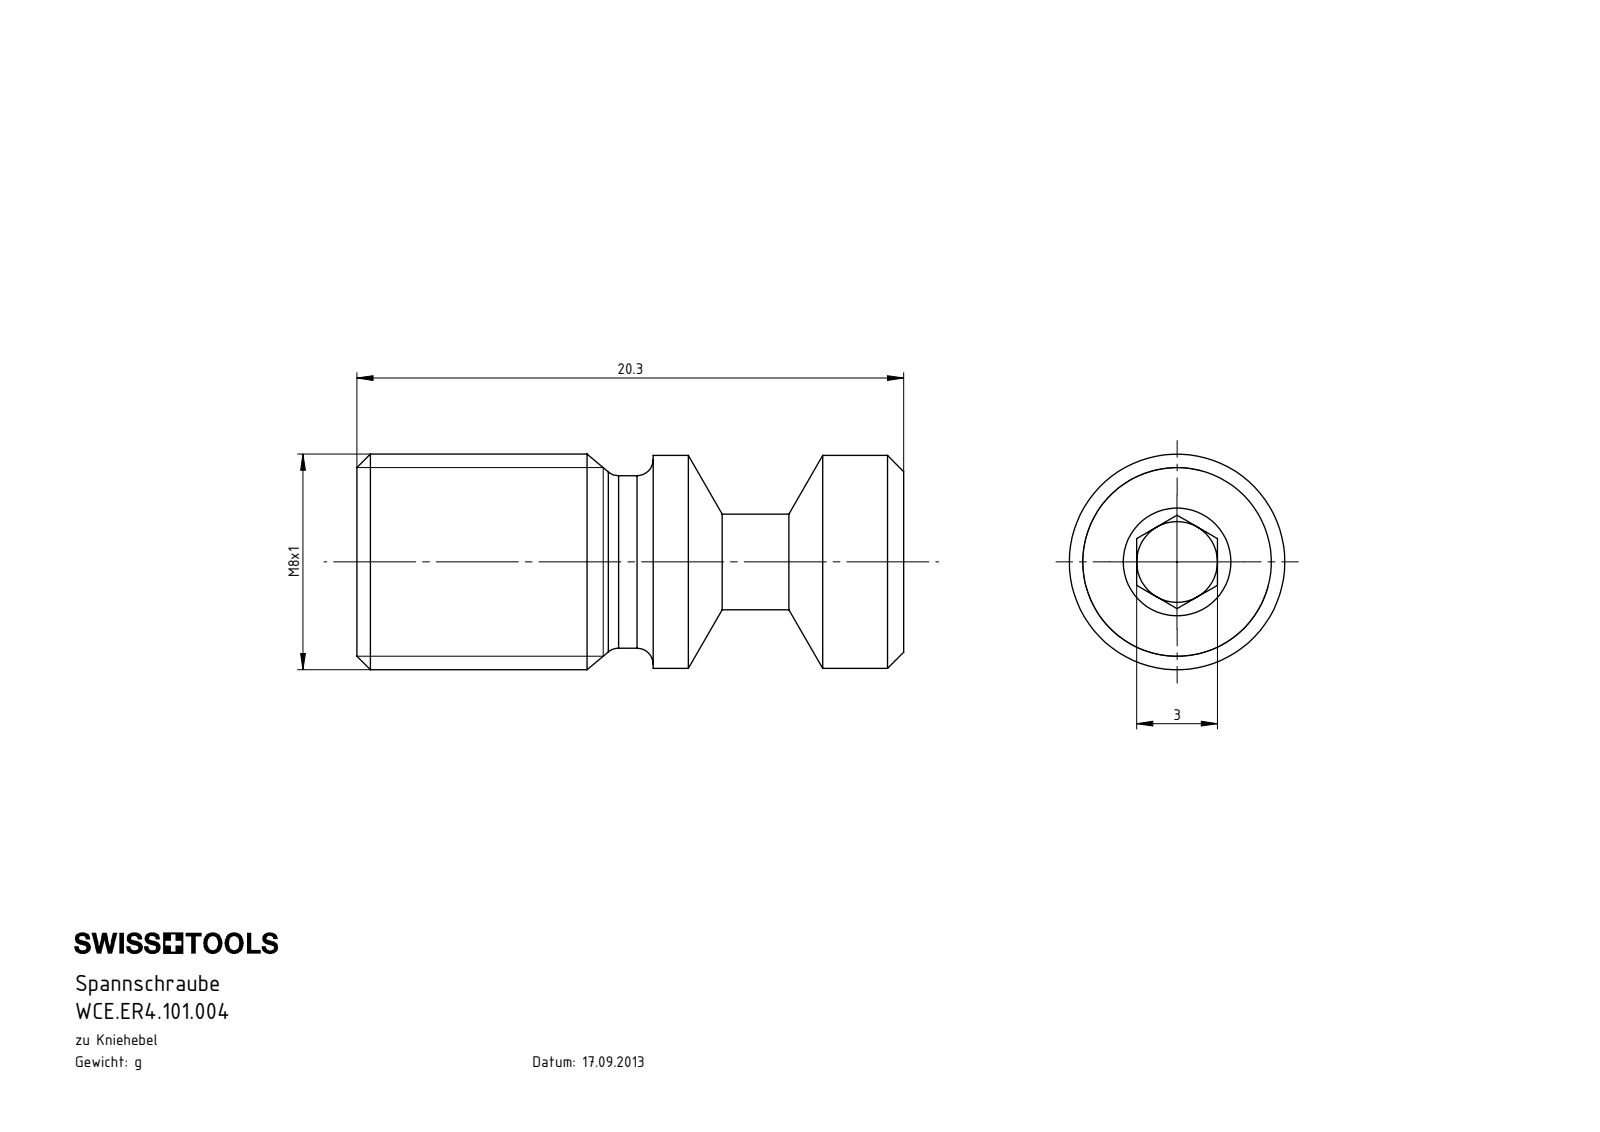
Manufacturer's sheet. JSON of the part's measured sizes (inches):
{"part_name": "WCE.ER4.101.004", "step_written_by": "SolidWorks 2017 (AUTOMOTIVE_DESIGN)", "units": "inches", "bodies": {"solids": 1, "faces": 29, "planar": 15, "cylindrical": 5, "other": 9}, "overall_size": [0.799, 0.315, 0.315], "volume_in3": 0.048, "surface_area_in2": 0.98, "round_bosses_or_shafts": [[0.315, 1], [0.311, 1], [0.252, 1], [0.14, 1]], "face_to_face_distances": [0.799, 0.118, 0.433, 0.366, 0.157, 0.276, 0.642]}
